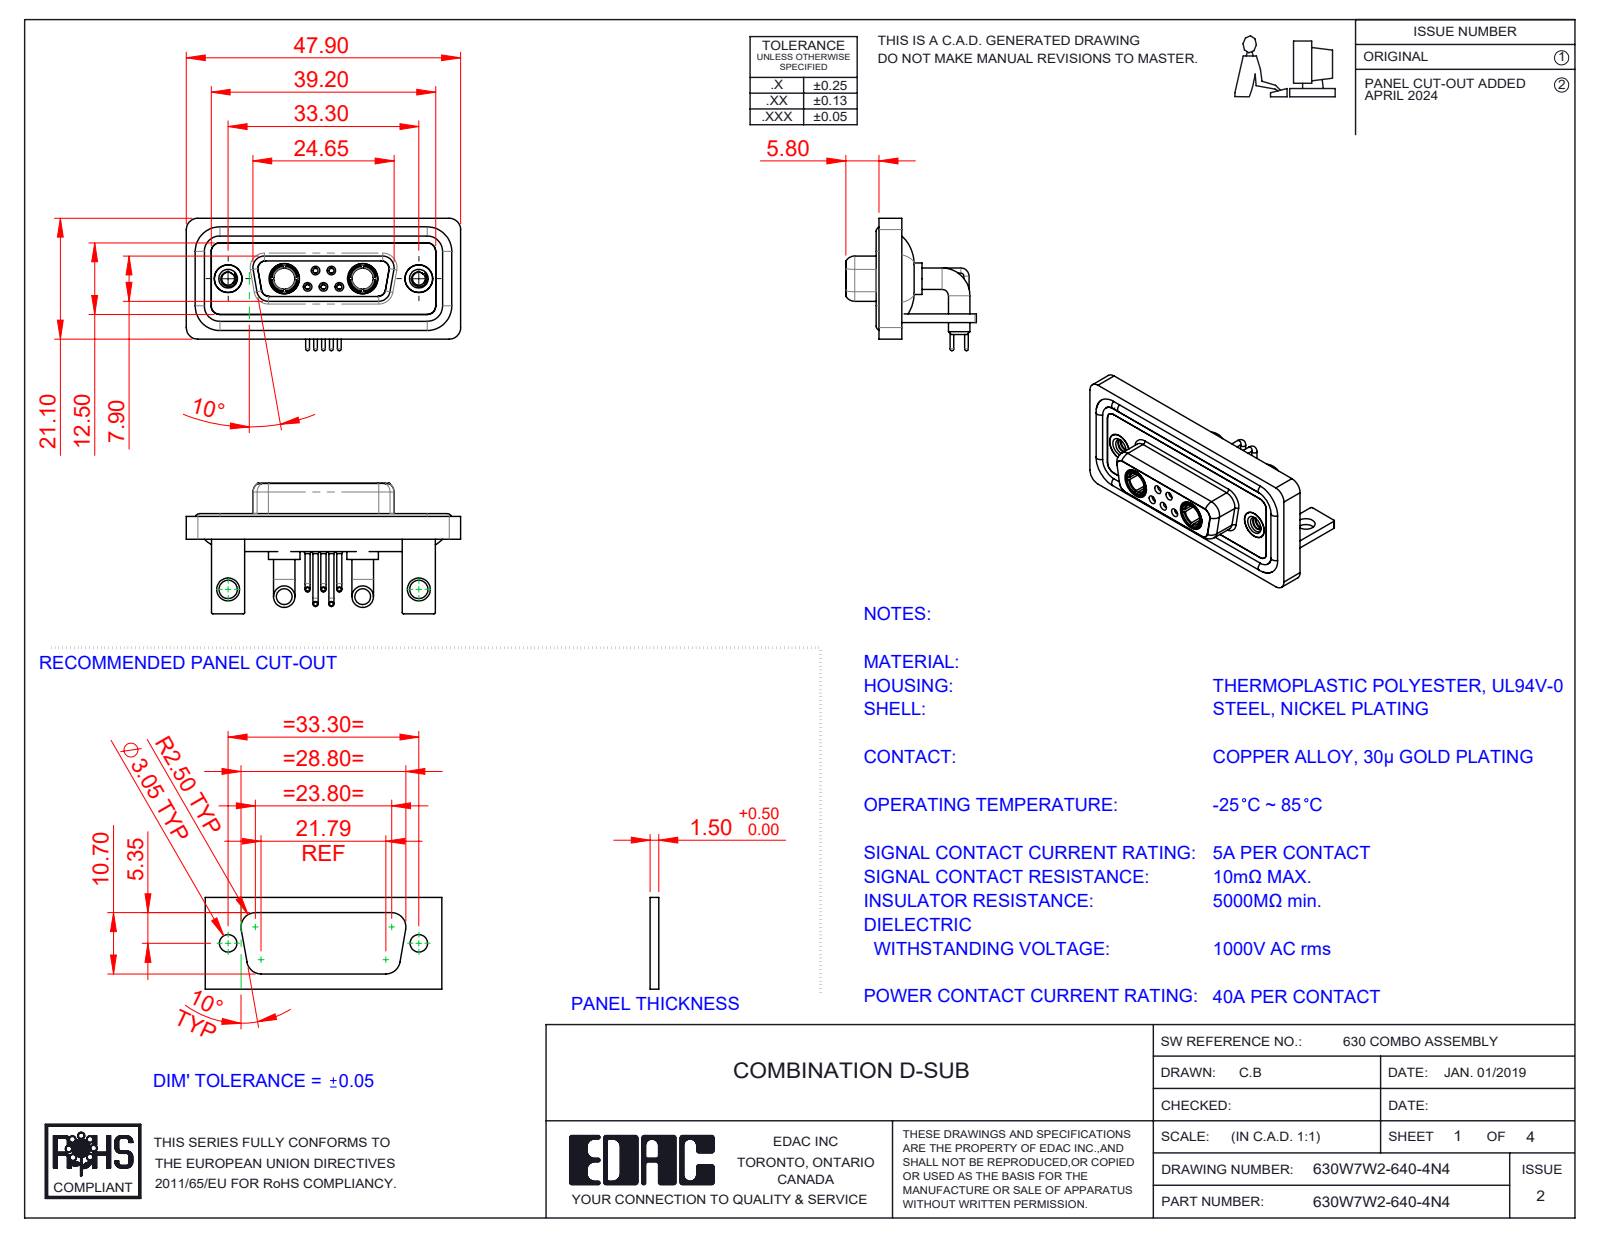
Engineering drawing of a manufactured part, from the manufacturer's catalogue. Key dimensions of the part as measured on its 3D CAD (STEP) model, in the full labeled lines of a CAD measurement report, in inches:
Part name (STEP PRODUCT): 630W7W2-640-4N4; 630Combo Contact Row 1_50 Contacts; 630Combo Housing_7W2; 630Combo Stabilizer Bracket_50 Contacts (+6 more)
STEP written by: SolidWorks 2023 (CONFIG_CONTROL_DESIGN)
Units: inches
Bodies: 18 solids, 855 faces (258 planar, 377 cylindrical, 220 other)
Overall size (bounding box): 1.886 × 0.91 × 0.898
Volume: 0.409 in³ · Surface area: 17.09 in²
Round holes (diameter × count): ⌀0.035 ×5, ⌀0.043 ×5, ⌀0.059 ×5, ⌀0.079 ×5, ⌀0.191 ×4, ⌀0.063 ×3, ⌀0.067 ×2, ⌀0.089 ×2, ⌀0.126 ×2, ⌀0.146 ×2, ⌀0.157 ×2, ⌀0.159 ×2
Round bosses / shafts (diameter × count): ⌀0.063 ×6, ⌀0.035 ×5, ⌀0.026 ×5, ⌀0.148 ×4, ⌀0.217 ×2, ⌀0.205 ×2, ⌀0.195 ×2, ⌀0.195 ×2
Partial cylindrical surfaces — rounded edges, fillets, slot ends (radius × count): R0.079 ×21, R0.059 ×18, R0.01 ×16, R0.053 ×12, R0.063 ×8, R0.02 ×5, R0.024 ×4, R0.026 ×4
Main face-to-face distances: 0.016, 0.114, 0.059, 0.071, 0.146, 0.043, 0.161, 0.063, 0.098, 0.055
Hole centre spacings: 0.124, 0.109, 0.386, 0.925, 1.311, 0.17, 0.17, 0.198
